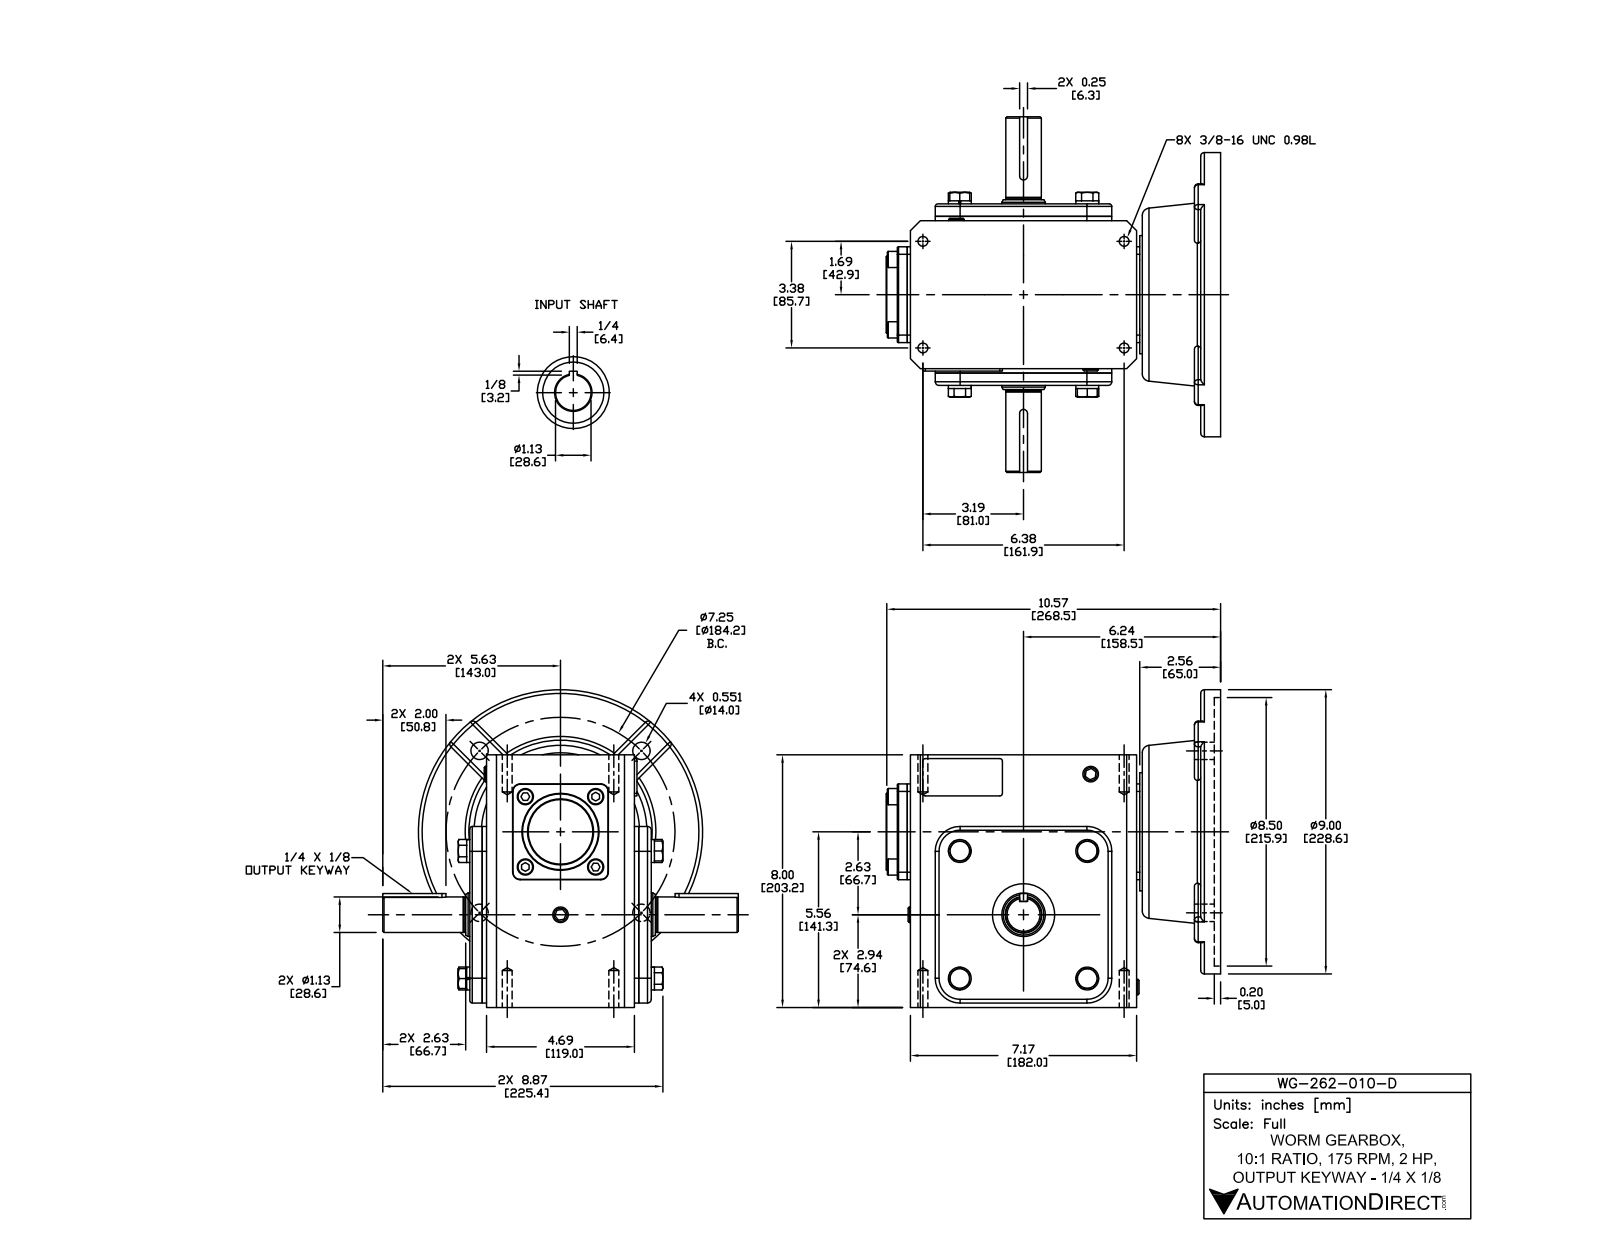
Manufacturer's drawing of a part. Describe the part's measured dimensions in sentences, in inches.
The part is named "WG-262-010-D". Its 3-D file was written by "SolidWorks 2015 (CONFIG_CONTROL_DESIGN)". It is 32 solids with 579 faces: 306 planar, 148 cylindrical and 125 other. Overall it measures 11.26 by 10.591 by 10.063 inches. Its volume is 333.4 cubic inches and its surface area 767.9 square inches. Round holes: 4 of diameter 0.313, 4 of diameter 0.551, 1 of diameter 0.591, 1 of diameter 1.125, 1 of diameter 1.378, 1 of diameter 1.969, 1 of diameter 2.047, 1 of diameter 3.819, 1 of diameter 8.5. Round bosses or shafts: 4 of diameter 0.724, 4 of diameter 0.512, 1 of diameter 9, 1 of diameter 2.441, 1 of diameter 1.772, 1 of diameter 1.142, 1 of diameter 1.125, 1 of diameter 1.113. Partial cylindrical surfaces (rounded edges, fillets, slot ends): 19 of radius 0.118, 7 of radius 0.079, 4 of radius 0.236, 4 of radius 0.787, 2 of radius 0.02, 2 of radius 0.039, 2 of radius 0.125. The main face-to-face distances are 4.961, 0.394, 5.354, 0.531, 5.217, 0.138, 4.823, 8, 0.433, 5.748. The hole center spacings are 3.625, 5.127, 2.564, 3.375, 5.787, 6.375, 7.213, 7.25.
